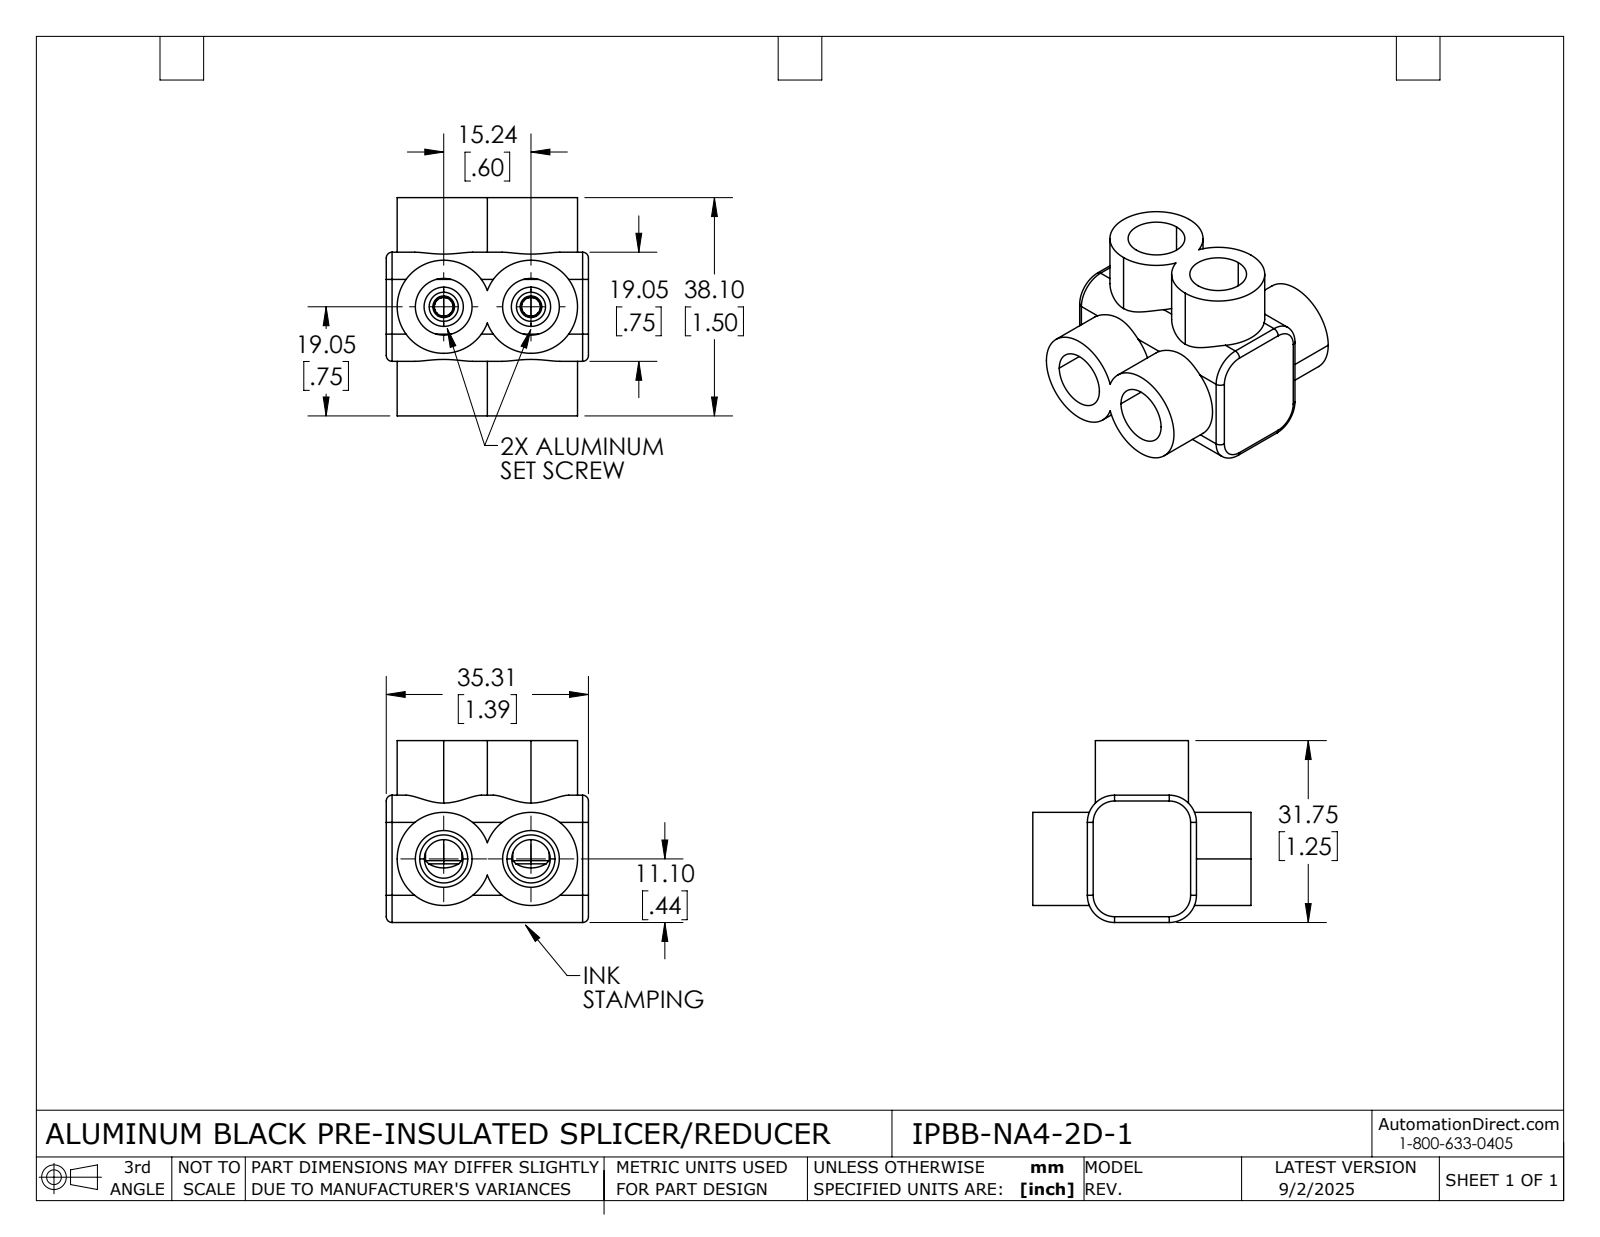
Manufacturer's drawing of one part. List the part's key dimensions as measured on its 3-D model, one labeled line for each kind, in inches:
Part name (STEP PRODUCT): IPBB-NA4-2D-1
STEP written by: SolidWorks 2024 (AUTOMOTIVE_DESIGN)
Units: inches
Bodies: 4 solids, 178 faces (74 planar, 64 cylindrical, 40 other)
Overall size (bounding box): 1.5 × 1.39 × 1.25
Volume: 1.185 in³ · Surface area: 19.27 in²
Round holes (diameter × count): ⌀0.39 ×4, ⌀0.129 ×2, ⌀0.213 ×2, ⌀0.265 ×2
Round bosses / shafts (diameter × count): ⌀0.64 ×4, ⌀0.25 ×2
Partial cylindrical surfaces — rounded edges, fillets, slot ends (radius × count): R0.04 ×8, R0.062 ×4, R0.187 ×4
Main face-to-face distances: 0.5, 0.125, 1.265, 1, 0.625, 1.14, 1.125, 0.75, 1.39, 1.25
Hole centre spacings: 0.6
